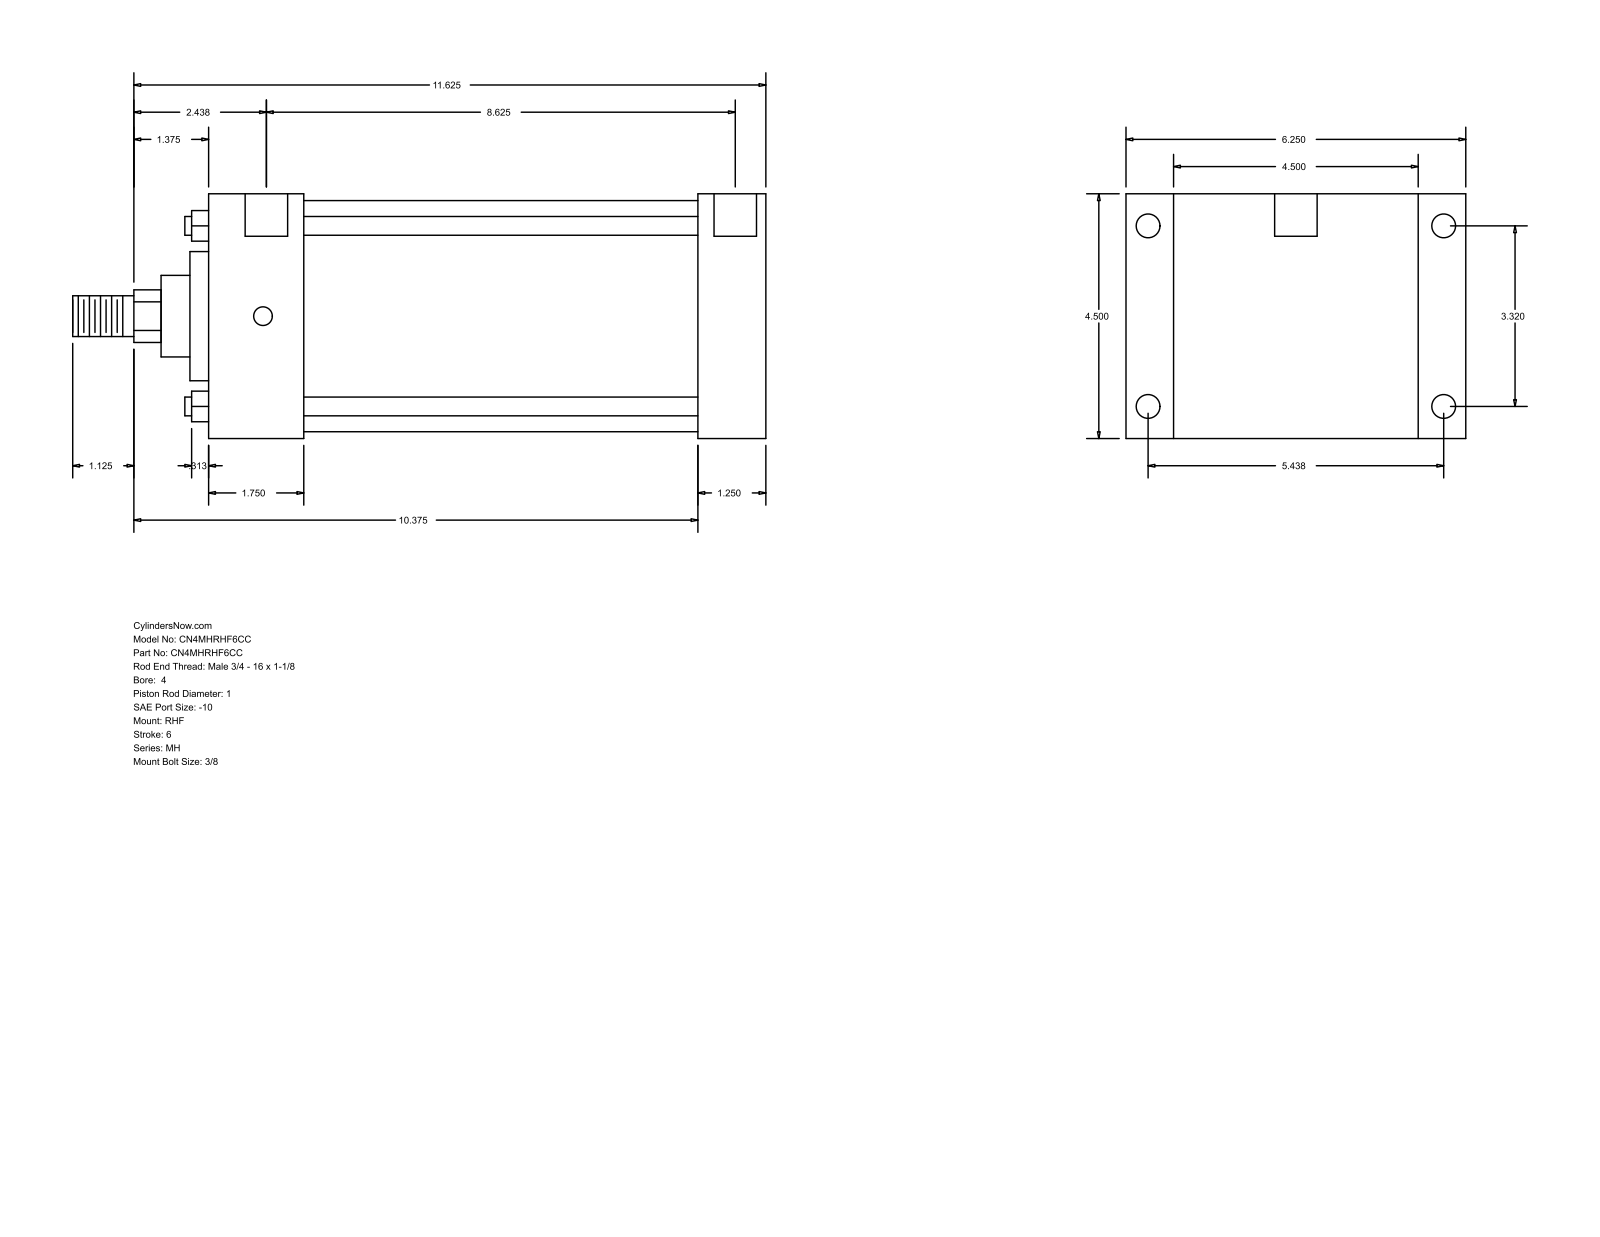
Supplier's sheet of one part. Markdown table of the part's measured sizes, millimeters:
| quantity | value |
| --- | --- |
| part name | MH_RHF__0400_1 |
| STEP written by | GSSL Pune (CONFIG_CONTROL_DESIGN) |
| units | millimeters |
| bodies | 0 solids, 90 faces (61 planar, 29 cylindrical, 0 other) |
| overall size | 323.85 × 158.75 × 114.3 |
| round holes (diameter × count) | 8.73 × 4, 11.13 × 4, 19.84 × 2 |
| round bosses / shafts (diameter × count) | 8.76 × 4, 107.95 × 1, 60.33 × 1, 38.1 × 1, 25.4 × 1, 19.05 × 1 |
| partial cylindrical surfaces (radius × count) | 12.29 × 1 |
| main face-to-face distances | 114.3, 260.35, 228.6, 31.75, 22.23, 136.53, 44.46, 184.14, 215.89, 158.76 |
| hole center spacings | 1.58, 84.32, 138.12, 161.82, 220.66, 222.24, 219.08 |
